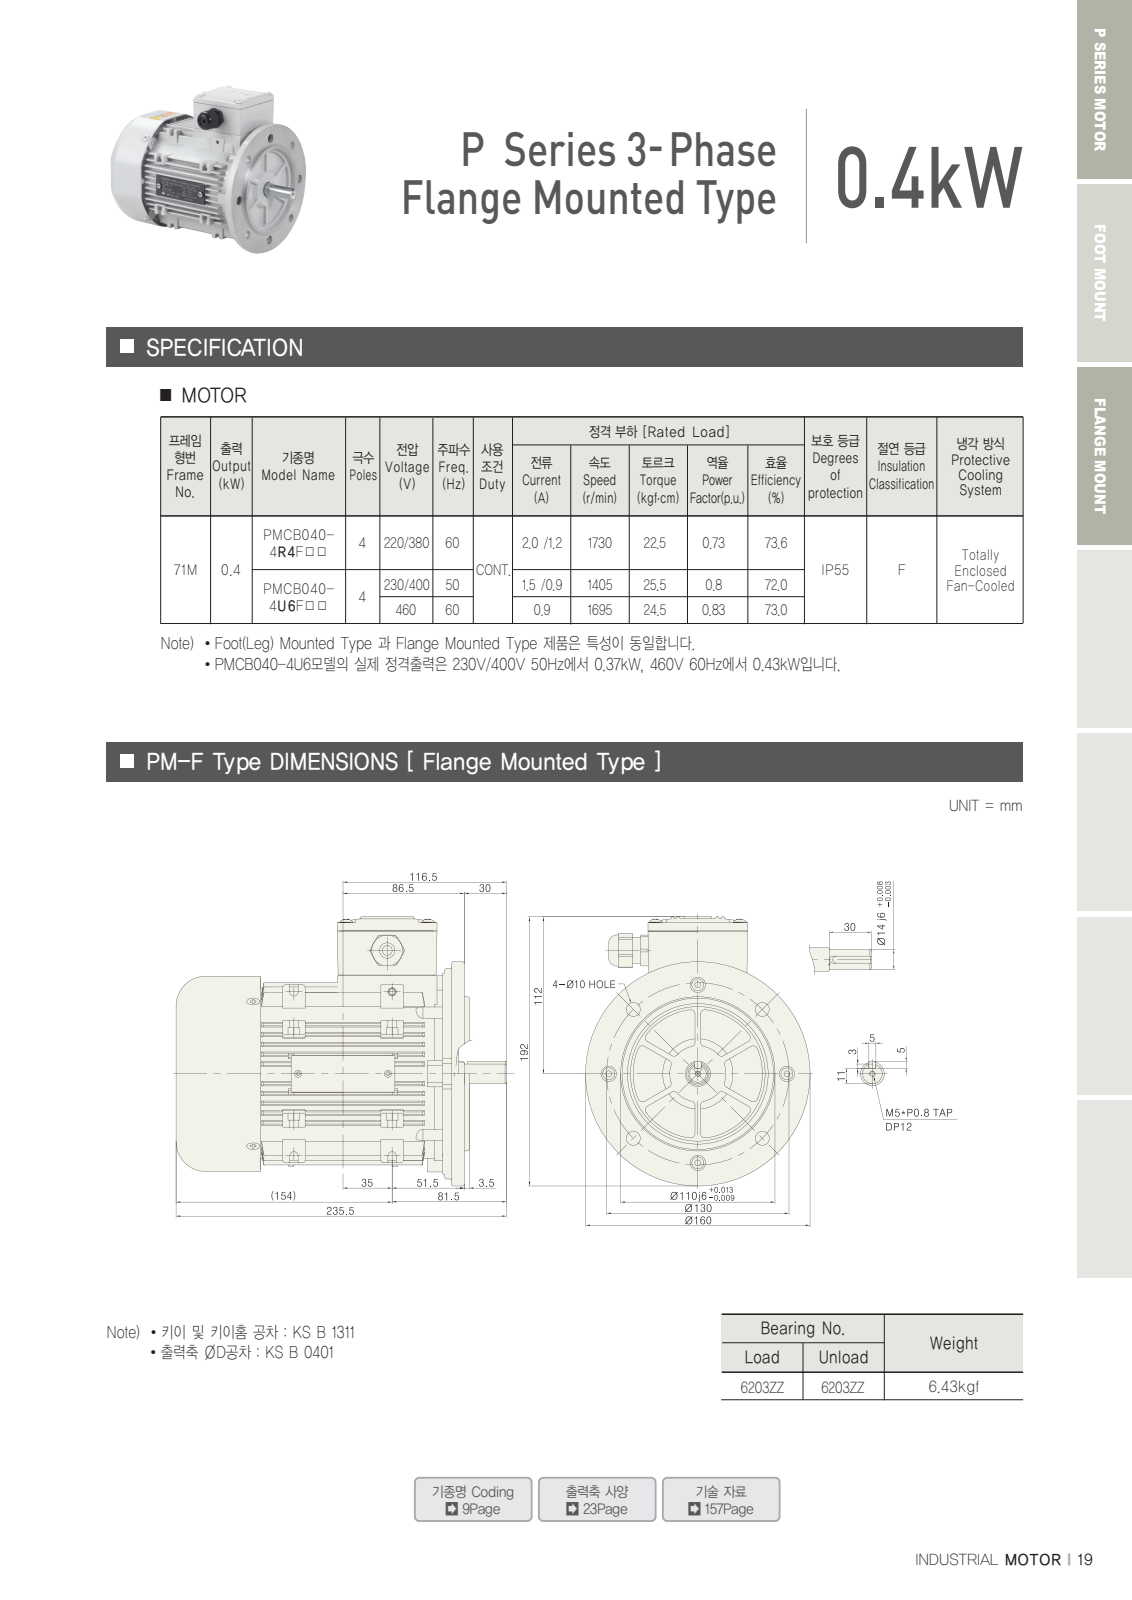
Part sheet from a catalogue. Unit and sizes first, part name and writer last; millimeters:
Units: millimetres
Overall size (bounding box): 235.5 × 194 × 160
Round holes (diameter × count): ⌀3.2 ×16, ⌀6 ×13, ⌀3.5 ×8, ⌀4.13 ×8, ⌀5 ×8, ⌀5.1 ×8, ⌀3.24 ×4, ⌀10 ×4, ⌀12 ×4, ⌀4.1 ×2, ⌀4.2 ×2, ⌀1.6 ×1
Round bosses / shafts (diameter × count): ⌀4 ×10, ⌀3.57 ×10, ⌀9.2 ×8, ⌀5 ×8, ⌀18.2 ×2, ⌀160 ×1, ⌀125 ×1, ⌀124 ×1
Partial cylindrical surfaces — rounded edges, fillets, slot ends (radius × count): R0.5 ×410, R3 ×63, R1 ×48, R2 ×17, R20 ×12, R21.2 ×12, R10 ×8, R4.5 ×6
Main face-to-face distances: 5, 150, 155, 9, 164, 1.2, 159, 3, 2.5, 4
Hole centre spacings: 48.6, 49.19, 53.46, 63.5, 89.8, 90.87, 117.33, 118.72
Volume: 782 540 mm³ · Surface area: 425 680 mm²
Bodies: 38 solids, 3300 faces (1465 planar, 1215 cylindrical, 620 other)
Part name (STEP PRODUCT): PMCB040-4R4F; 71M 400W FRAME L_T; SHAFT 20081024; 71M 400W REAR COVER L-T (+8 more)
STEP written by: Autodesk Inventor 2011 (AUTOMOTIVE_DESIGN)
